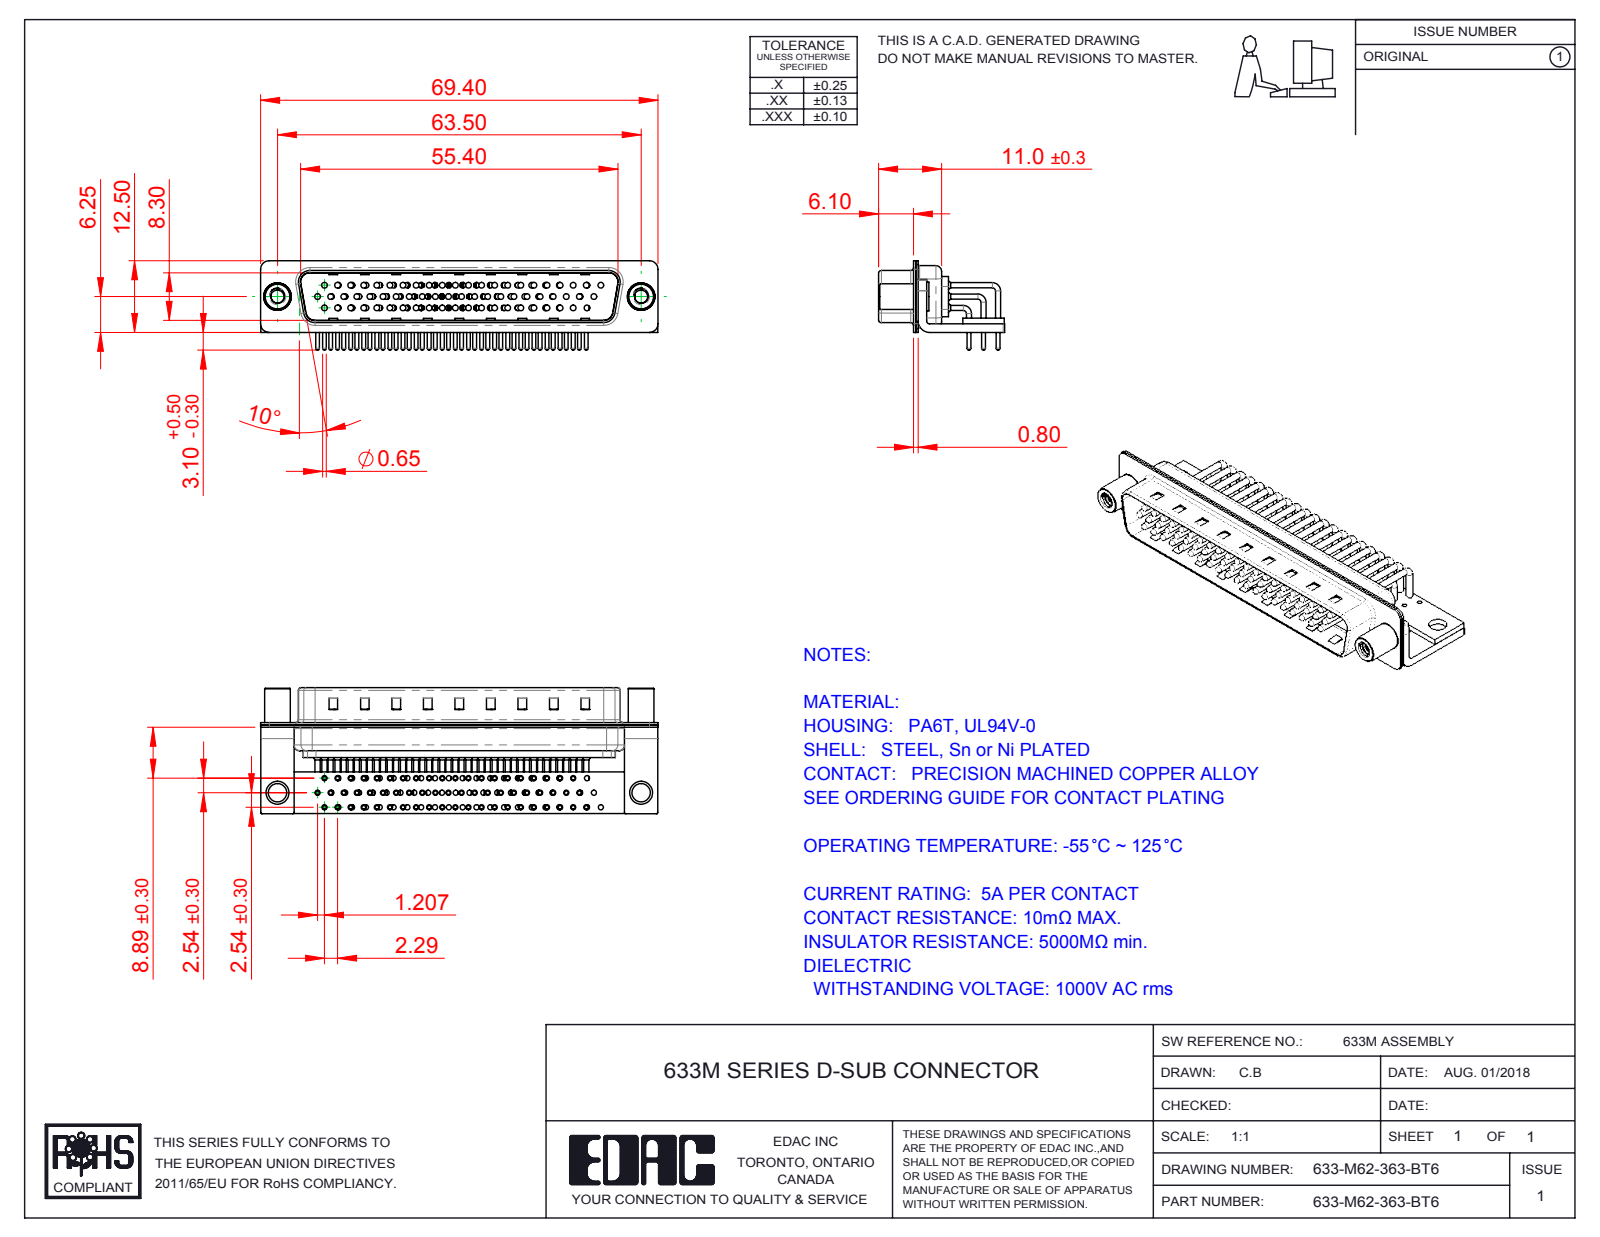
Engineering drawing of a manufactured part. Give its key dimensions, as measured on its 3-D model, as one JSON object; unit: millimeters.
{"part_name": "633M Stabilizer Bracket; 633M 4-40 Threaded Standoff; 633M Stabilizer Board_62 Contacts; 633M Shell Front_62 Contacts (+6 more)", "step_written_by": "SolidWorks 2016 (CONFIG_CONTROL_DESIGN)", "units": "millimeters", "bodies": {"solids": 70, "faces": 7456, "planar": 4199, "cylindrical": 2561, "other": 696}, "overall_size": [69.4, 22, 15.6], "volume_mm3": 5201, "surface_area_mm2": 15819, "round_holes": [[0.9, 62], [1, 62], [1.7, 62], [2, 62], [2.26, 2], [3.2, 2], [4, 2], [4.8, 2]], "round_bosses_or_shafts": [[0.9, 118], [1.5, 62], [0.65, 62], [1, 56], [5, 2], [4.9, 2], [4.5, 2]], "partial_cylinders_radius": [[1.01, 62], [0.25, 16], [1.5, 16], [2, 13], [0.5, 9], [1.6, 8], [0.6, 4], [0.65, 4]], "face_to_face_distances": [0.4, 0.85, 1.25, 1.5, 9.55, 1, 1.9, 10.4, 8.3, 0.8], "hole_center_spacings": [7.24, 2.41, 9.65, 4.83, 14.48, 16.89, 2.81, 2.32]}
